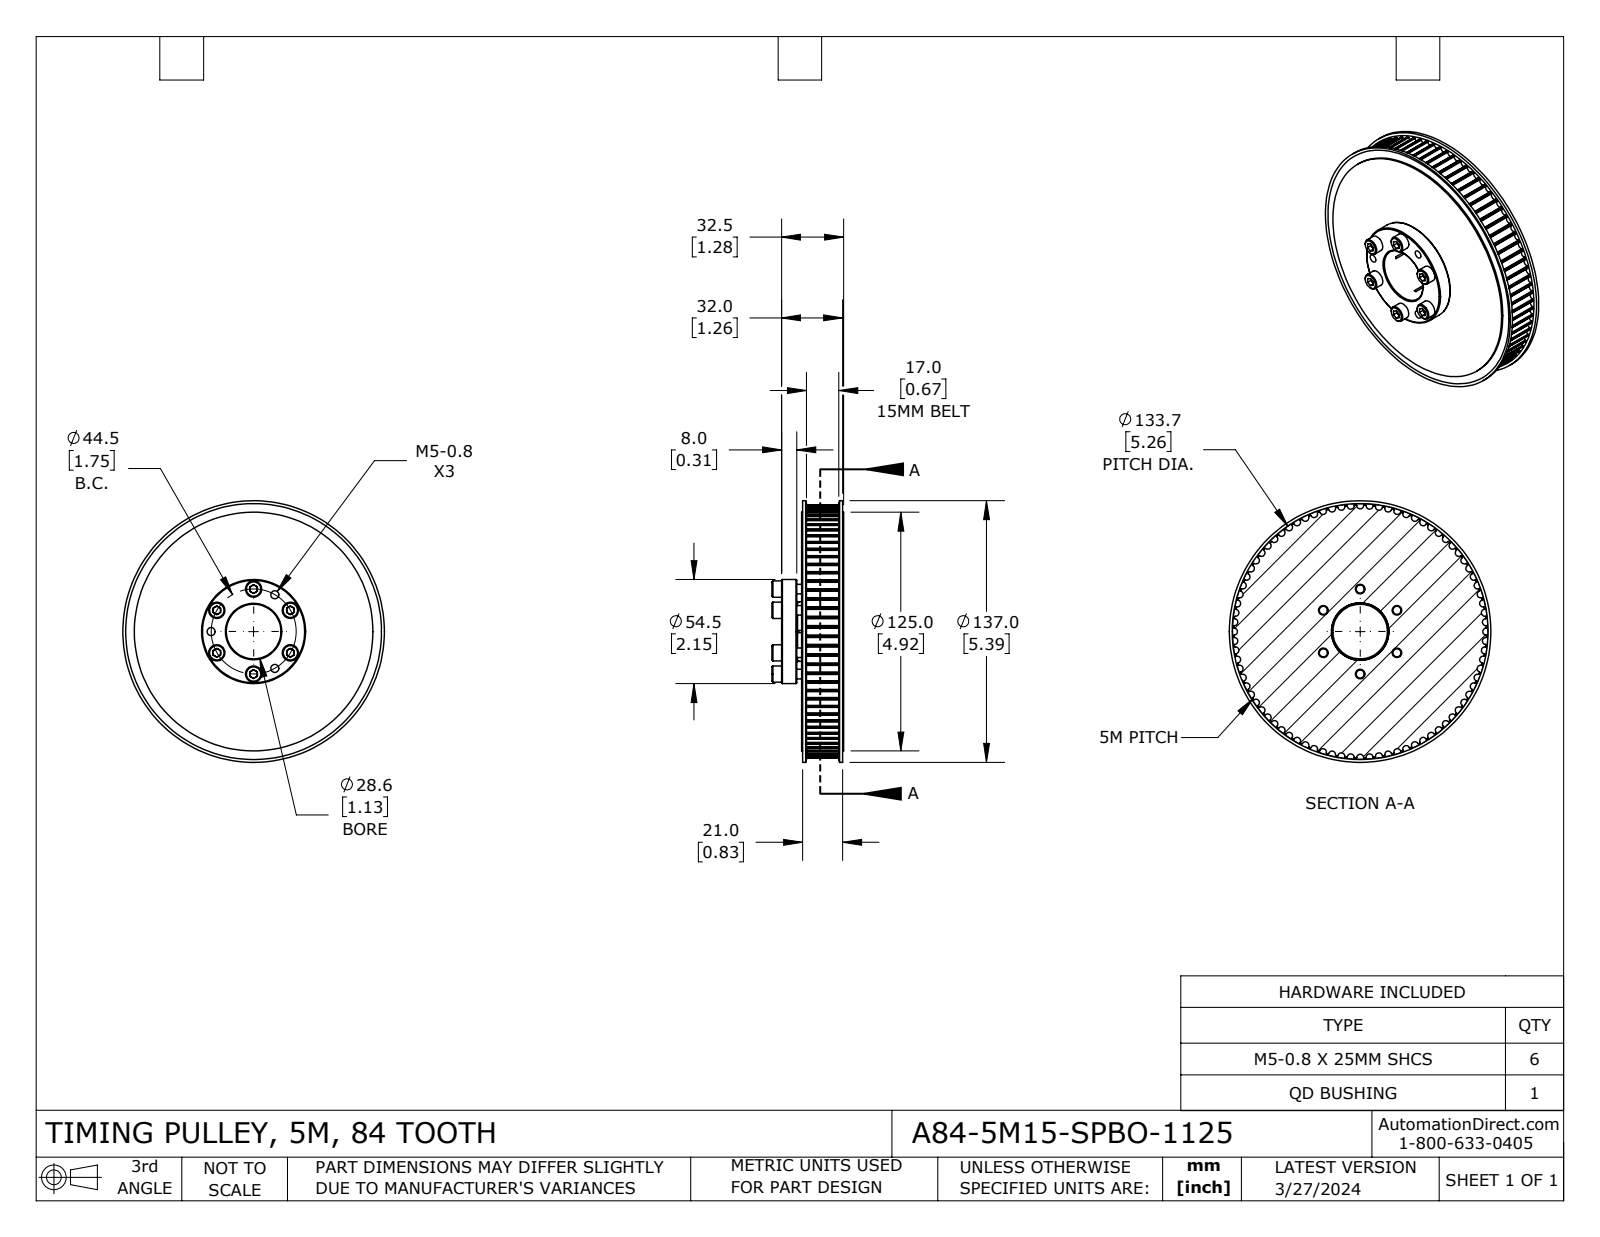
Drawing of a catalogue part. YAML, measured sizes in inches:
part_name: "A84-5M15-SPBO-1125"
step_written_by: "SolidWorks 2021 (CONFIG_CONTROL_DESIGN)"
units: inches
bodies: {solids: 10, faces: 673, planar: 116, cylindrical: 495, other: 62}
overall_size: [5.394, 5.394, 1.476]
volume: 18.06
surface_area: 103.2
round_holes:
  - {diameter: 0.165, count: 9}
  - {diameter: 0.217, count: 6}
  - {diameter: 1.125, count: 1}
  - {diameter: 1.125, count: 1}
  - {diameter: 1.228, count: 1}
  - {diameter: 4.921, count: 1}
round_bosses_or_shafts:
  - {diameter: 0.335, count: 6}
  - {diameter: 0.197, count: 6}
  - {diameter: 5.394, count: 1}
  - {diameter: 2.146, count: 1}
  - {diameter: 1.227, count: 1}
partial_cylinders:
  - {radius: 0.012, count: 168}
  - {radius: 0.072, count: 84}
  - {radius: 2.609, count: 1}
face_to_face_distances: [0.866, 0.098, 0.768, 0.035, 0.831, 0.063, 0.732, 0.669, 0.795, 0.512]
hole_center_spacings: [0.876, 1.517, 1.752, 1.239, 1.693, 0.454, 1.517, 0.453]
